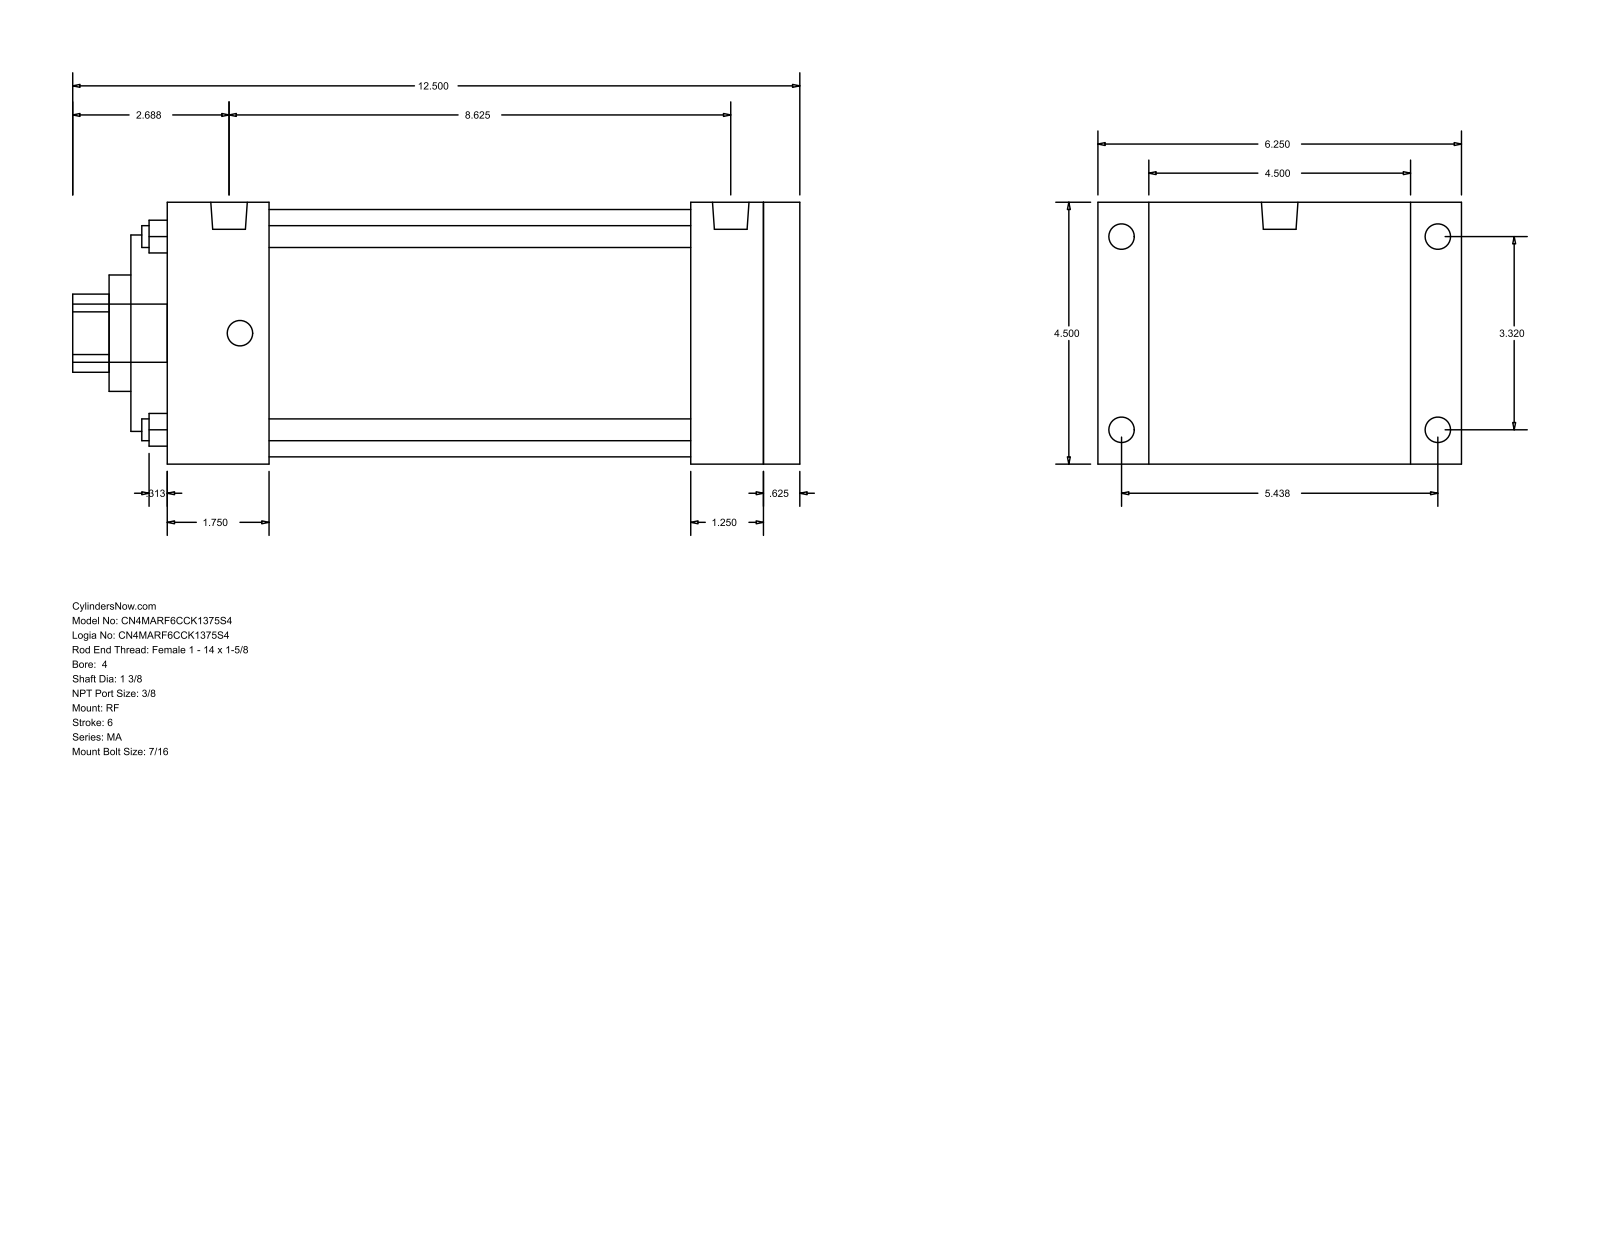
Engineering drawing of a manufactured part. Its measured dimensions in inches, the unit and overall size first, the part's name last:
Units: inches
Overall size (bounding box): 12.5 × 6.25 × 4.5
Round holes (diameter × count): ⌀0.375 ×4, ⌀1.375 ×1, ⌀2 ×1, ⌀3.375 ×1, ⌀4.25 ×1
Round bosses / shafts (diameter × count): ⌀0.437 ×8, ⌀0.627 ×2, ⌀1 ×1
Partial cylindrical surfaces — rounded edges, fillets, slot ends (radius × count): R0.672 ×1
Main face-to-face distances: 4.5, 10.875, 0.625, 10.25, 0.625, 10.875, 11.5, 0.875, 5.375, 9.625
Hole centre spacings: 2.347, 3.32, 4.695
Bodies: 0 solids, 94 faces (65 planar, 29 cylindrical, 0 other)
Part name (STEP PRODUCT): MA_RF__0400_1.375
STEP written by: GSSL Pune (CONFIG_CONTROL_DESIGN)
